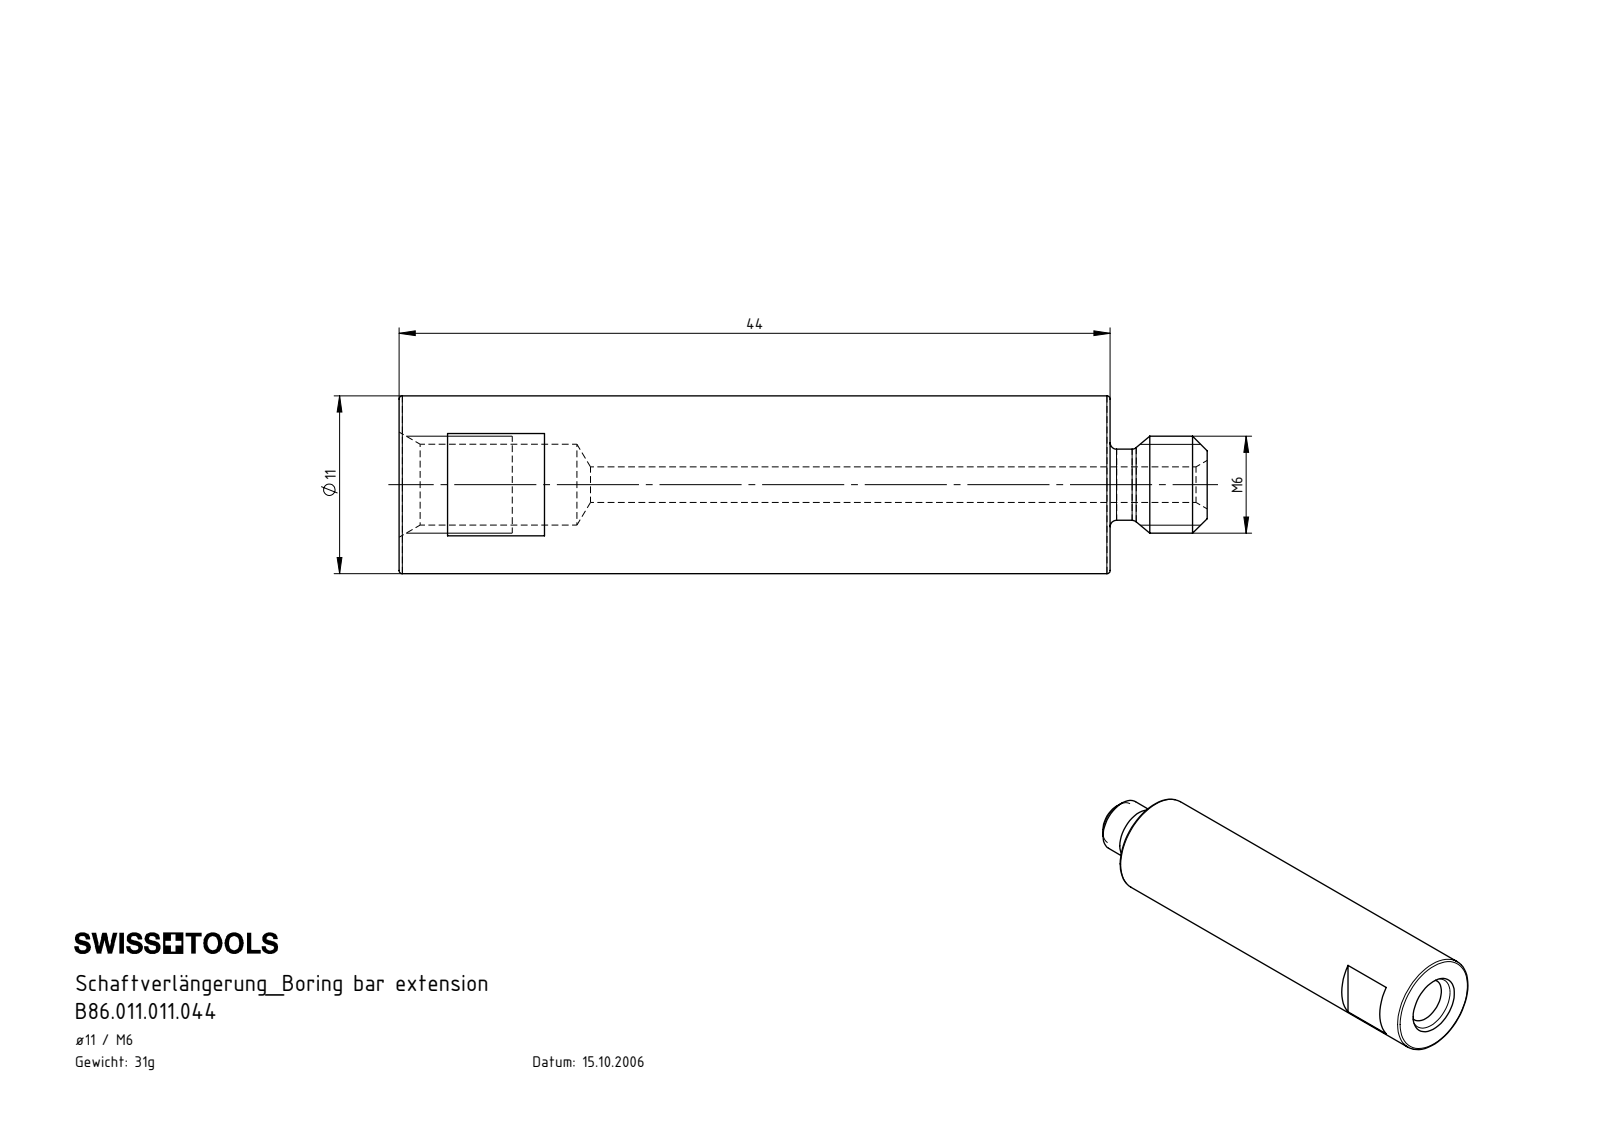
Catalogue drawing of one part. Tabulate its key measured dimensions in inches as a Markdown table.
| quantity | value |
| --- | --- |
| part name | B86.011.011.044 |
| STEP written by | SolidWorks 2022 (CONFIG_CONTROL_DESIGN) |
| units | inches |
| bodies | 1 solid, 37 faces (9 planar, 10 cylindrical, 18 other) |
| overall size | 1.969 × 0.433 × 0.433 |
| volume | 0.237 in³ |
| surface area | 3.484 in² |
| round holes (diameter × count) | 0.087 × 1, 0.197 × 1 |
| round bosses / shafts (diameter × count) | 0.433 × 1, 0.236 × 1, 0.173 × 1 |
| main face-to-face distances | 1.732, 0.354, 1.614, 0.236, 0.118, 1.378, 1.85, 1.969 |
